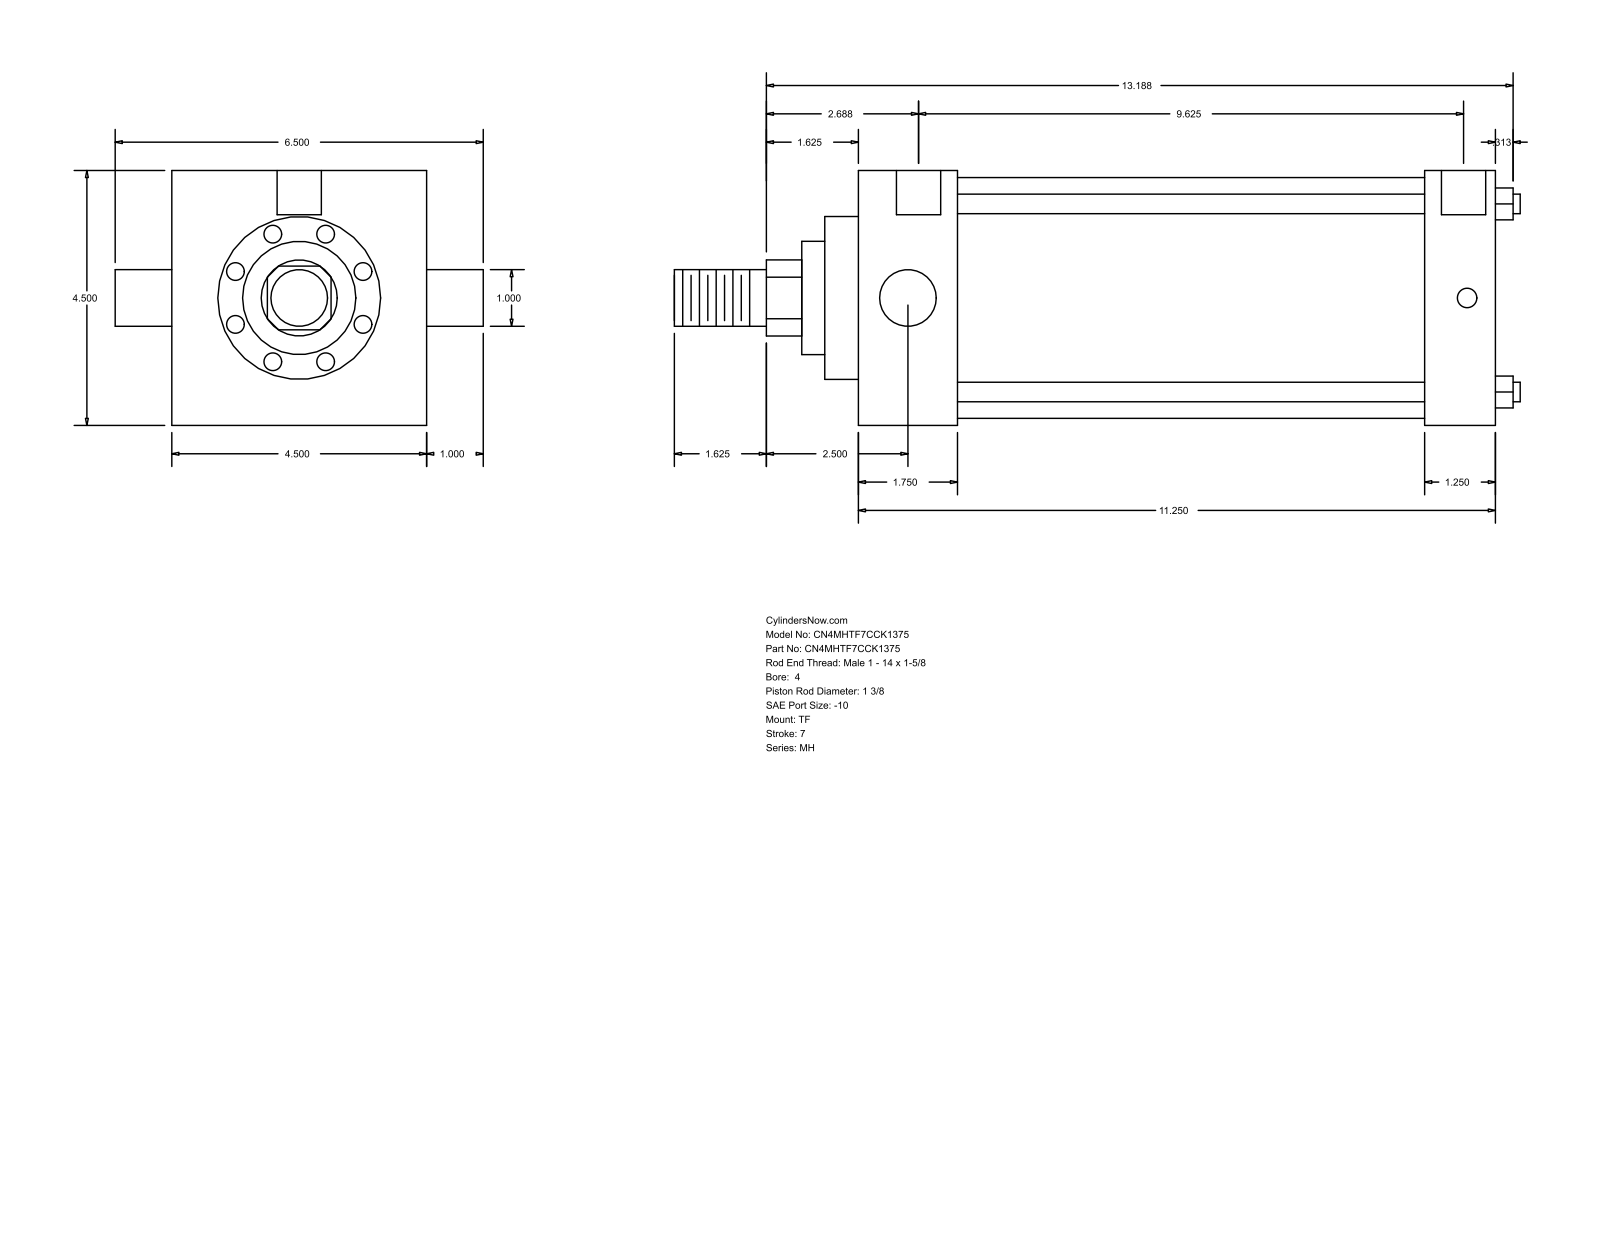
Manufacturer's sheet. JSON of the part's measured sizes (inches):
{"part_name": "MH_TF__0400_1.375", "step_written_by": "GSSL Pune (CONFIG_CONTROL_DESIGN)", "units": "inches", "bodies": {"solids": 0, "faces": 86, "planar": 61, "cylindrical": 25, "other": 0}, "overall_size": [14.937, 6.5, 4.5], "round_holes": [[0.344, 3], [0.781, 2]], "round_bosses_or_shafts": [[0.345, 4], [1, 2], [4.25, 1], [2.875, 1], [2, 1], [1.375, 1]], "partial_cylinders_radius": [[0.672, 1]], "face_to_face_distances": [4.5, 11.25, 1.75, 9.5, 10, 8.25, 1.25, 0.594, 2.344, 10.594], "hole_center_spacings": [0.062, 0.063, 9.625, 9.687, 9.688, 9.75]}
